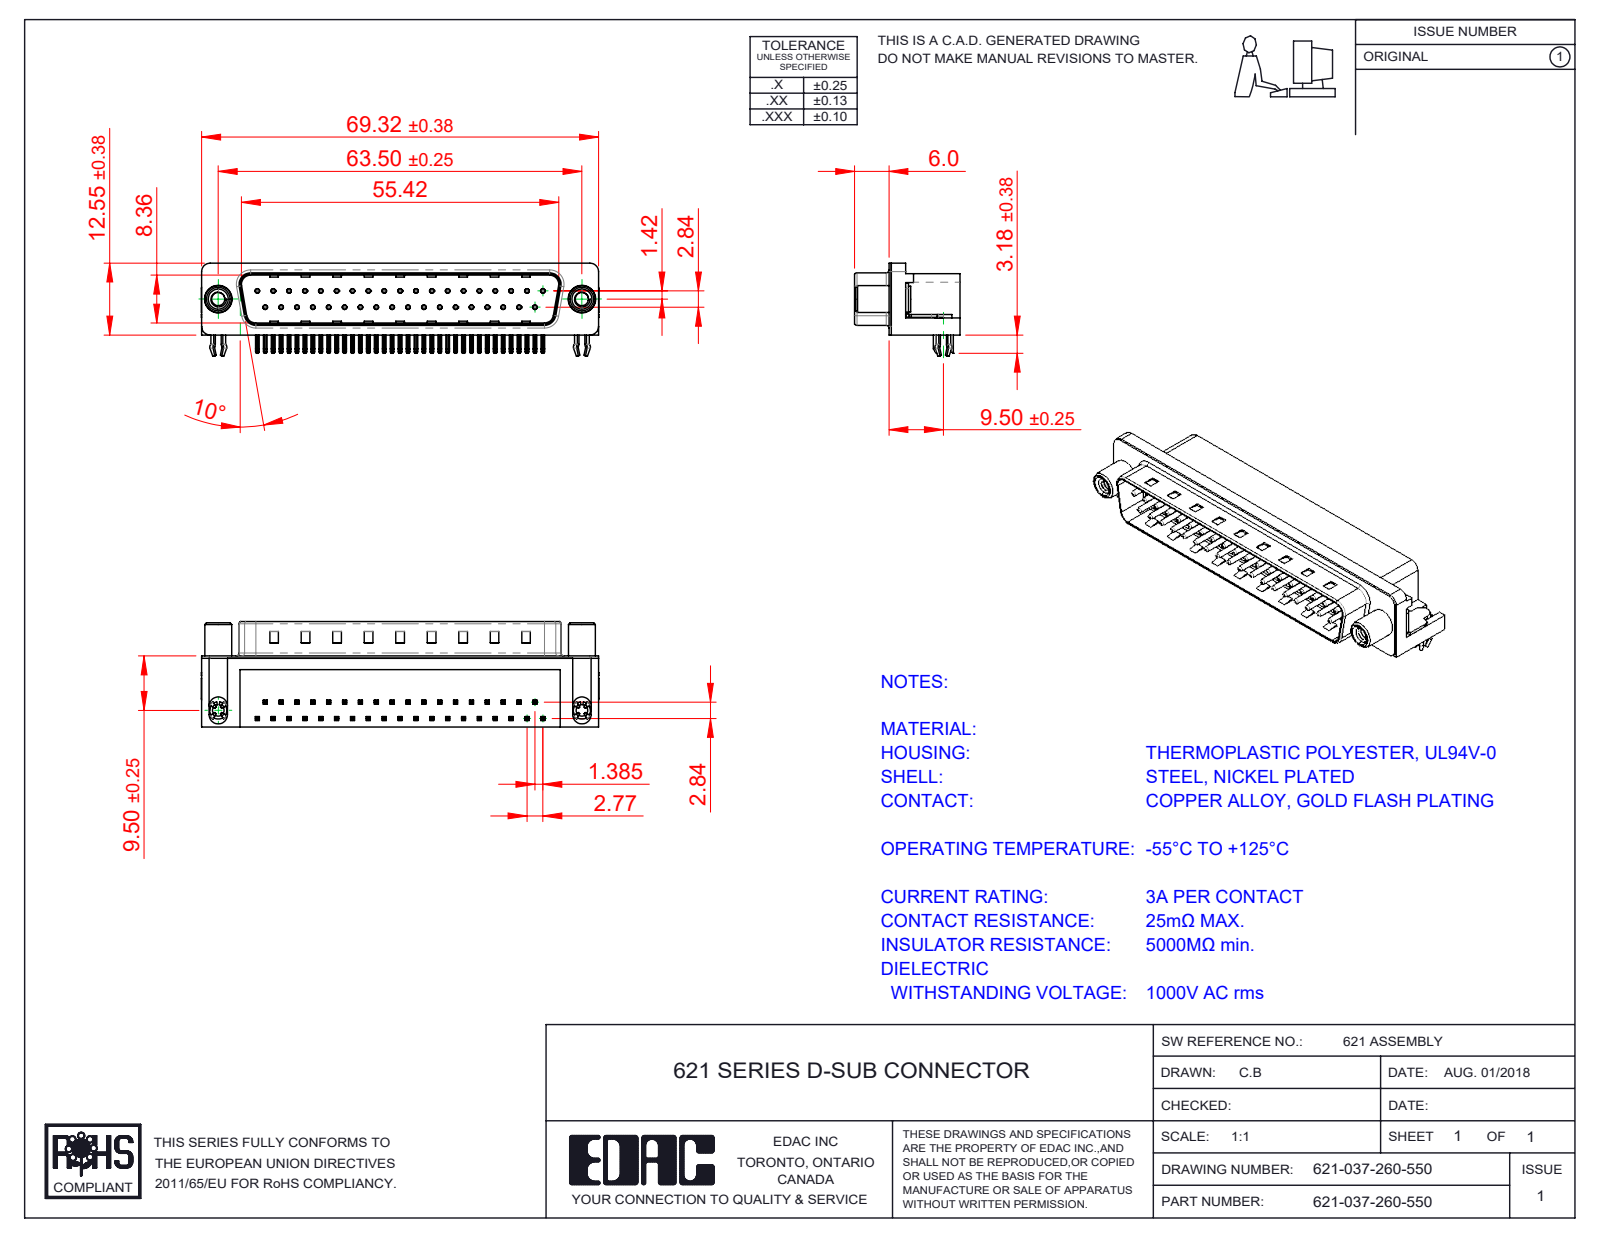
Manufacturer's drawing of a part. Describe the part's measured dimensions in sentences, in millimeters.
The part is named "621 Contact Bottom; 621 Shell_37 Socket; 621 4-40 Threaded Board Mount; 621 Round Threaded Standoff (+3 more)". Its 3-D file was written by "SolidWorks 2016 (CONFIG_CONTROL_DESIGN)". It is 43 solids with 3223 faces: 2005 planar, 935 cylindrical and 283 other. Overall it measures 69.4 by 18.4 by 15.73 millimeters. Its volume is 8 723 cubic millimeters and its surface area 10 373 square millimeters. Round holes: 37 of diameter 0.35, 37 of diameter 0.8, 2 of diameter 2.26, 2 of diameter 2.3, 2 of diameter 3.1, 2 of diameter 4, 2 of diameter 4.8, 2 of diameter 5. Round bosses or shafts: 37 of diameter 0.75, 2 of diameter 4.9, 2 of diameter 4.7, 2 of diameter 4.5, 2 of diameter 3.85, 2 of diameter 3.26. Partial cylindrical surfaces (rounded edges, fillets, slot ends): 148 of radius 0.25, 74 of radius 0.12, 16 of radius 1, 9 of radius 0.5, 8 of radius 1.6, 7 of radius 1.5, 4 of radius 0.9, 4 of radius 2. The main face-to-face distances are 0.4, 12, 10.35, 8.76, 2.1, 1.7, 10.46, 10.86, 9, 12.4. The hole center spacings are 3.16, 2.77, 5.54, 8.31, 11.08, 13.85, 19.39, 22.16.
